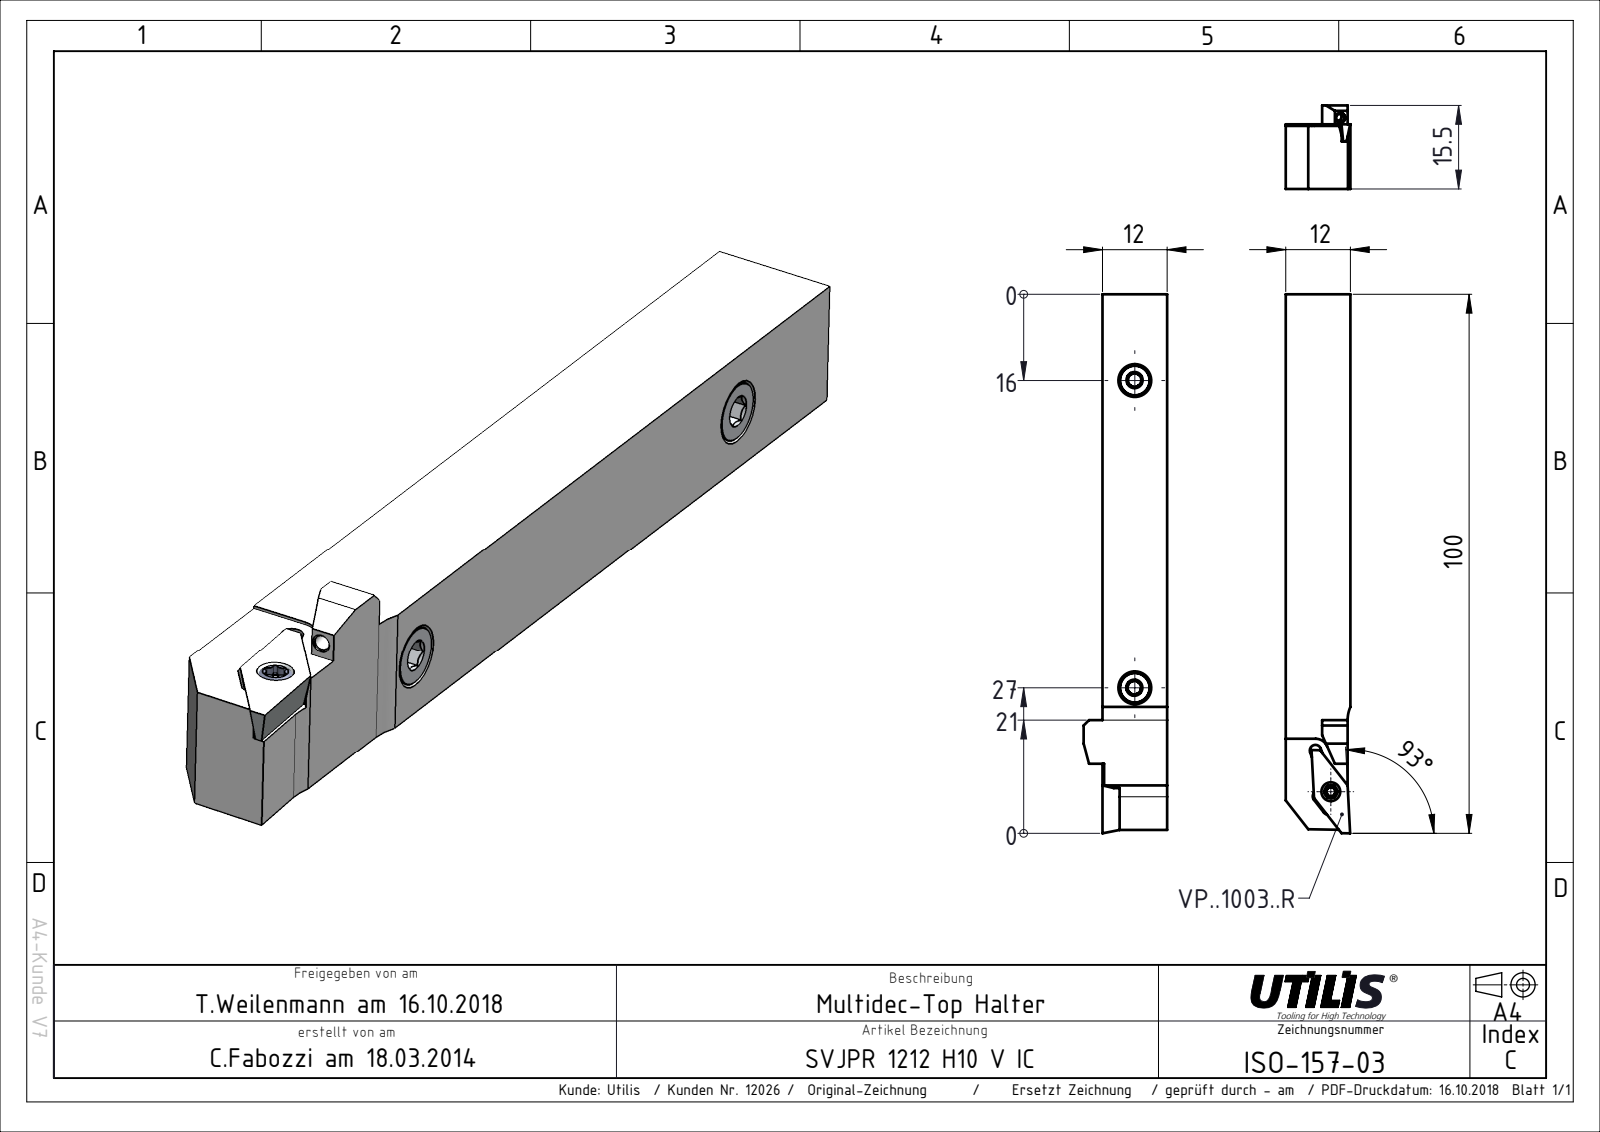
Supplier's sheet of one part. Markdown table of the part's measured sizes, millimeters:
| quantity | value |
| --- | --- |
| part name | ISO-157-03 |
| STEP written by | SolidWorks 2015 (AUTOMOTIVE_DESIGN) |
| units | millimeters |
| bodies | 1 solid, 59 faces (52 planar, 7 cylindrical, 0 other) |
| overall size | 100 × 15.5 × 12.2 |
| volume | 14 105 mm³ |
| surface area | 5 168 mm² |
| partial cylindrical surfaces (radius × count) | 1.05 × 3, 6.1 × 2, 2.3 × 1 |
| main face-to-face distances | 12, 11.73, 11.7, 15.5, 3.8, 3.5, 8.82, 2.88, 3.18, 6.68 |
